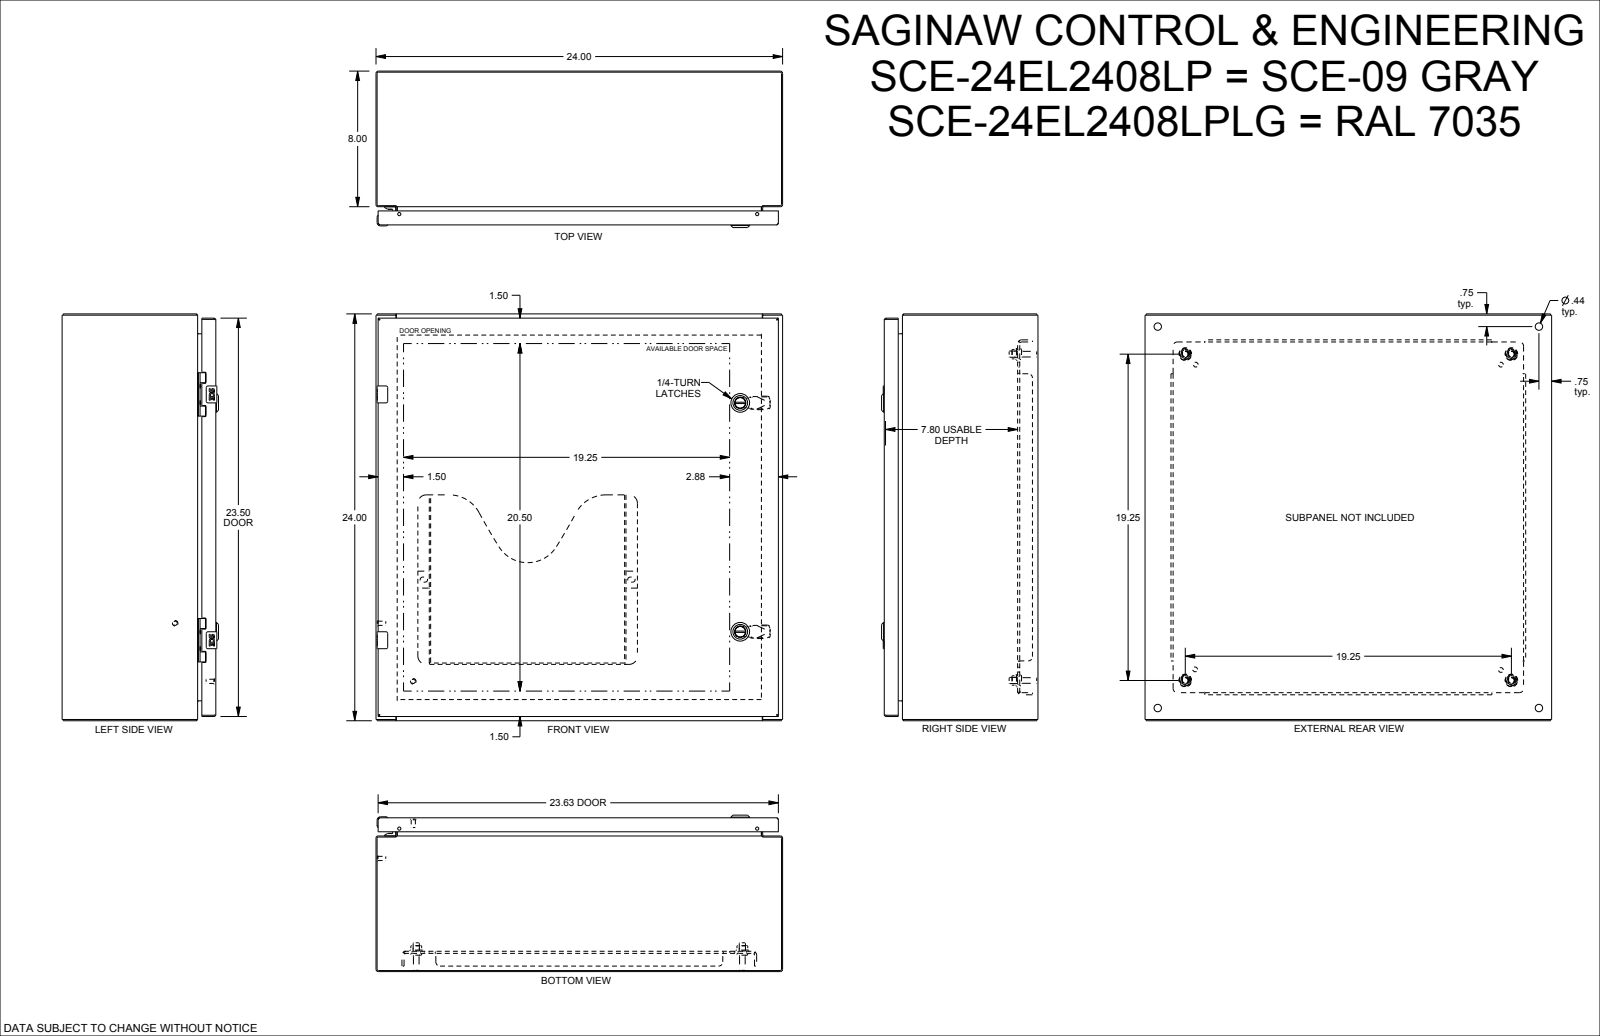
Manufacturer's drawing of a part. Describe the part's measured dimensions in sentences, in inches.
The part is named "SCE-24EL2408LP". Its 3-D file was written by "SolidWorks 2021 (AUTOMOTIVE_DESIGN)". It is 45 solids with 2819 faces: 1099 planar, 850 cylindrical and 870 other. Overall it measures 24 by 24 by 9.23 inches. Its volume is 239.8 cubic inches and its surface area 5 771 square inches. Round holes: 4 of diameter 0.172, 4 of diameter 0.205, 4 of diameter 0.244, 4 of diameter 0.266, 4 of diameter 0.281, 4 of diameter 0.367, 4 of diameter 0.375, 4 of diameter 0.437, 4 of diameter 0.5, 2 of diameter 0.04, 2 of diameter 0.188, 2 of diameter 0.197. Round bosses or shafts: 6 of diameter 0.17, 4 of diameter 0.366, 4 of diameter 0.332, 4 of diameter 0.25, 4 of diameter 0.248, 4 of diameter 0.24, 3 of diameter 0.196, 2 of diameter 1.102. Partial cylindrical surfaces (rounded edges, fillets, slot ends): 56 of radius 0.012, 28 of radius 0.01, 24 of radius 0.015, 20 of radius 0.02, 17 of radius 0.04, 13 of radius 0.06, 12 of radius 0.029, 12 of radius 0.1. The main face-to-face distances are 0.075, 23.925, 0.06, 9.073, 8.998, 9.013, 8.938, 1.2, 7.873, 1. The hole center spacings are 20.938, 18.641, 0.985, 14.5, 20.38, 0.875, 19.25, 0.02.
